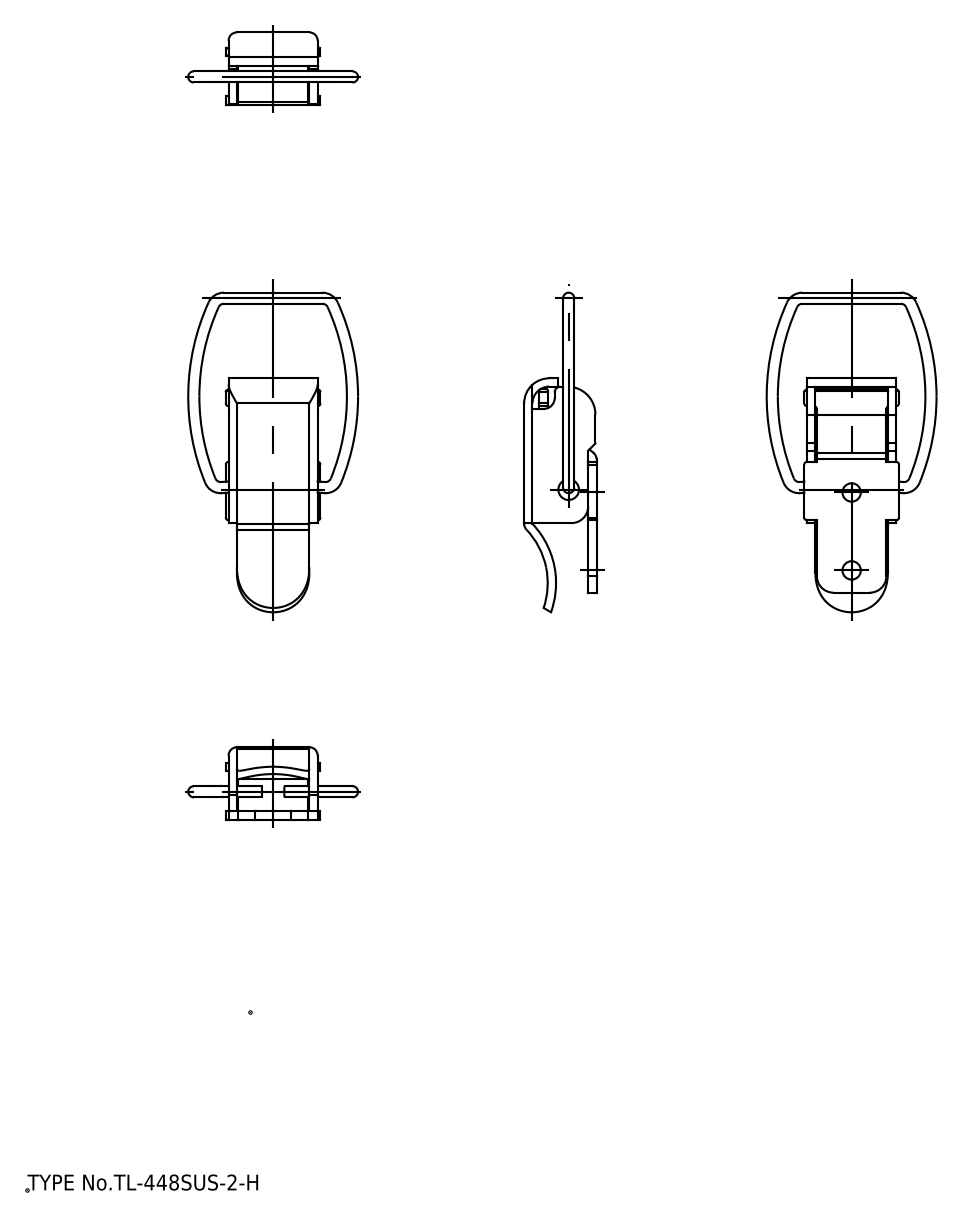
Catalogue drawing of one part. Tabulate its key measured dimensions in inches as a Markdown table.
| quantity | value |
| --- | --- |
| part name | アーム; ベース; レバー |
| STEP written by | spGate 20.6.3 (****-****-****-****) (AUTOMOTIVE_DESIGN) |
| units | inches |
| bodies | 3 solids, 110 faces (51 planar, 47 cylindrical, 12 other) |
| overall size | 2.259 × 1.201 × 0.512 |
| volume | 0.171 in³ |
| surface area | 6.91 in² |
| round holes (diameter × count) | 0.13 × 2, 0.146 × 1 |
| round bosses / shafts (diameter × count) | 0.079 × 3 |
| partial cylindrical surfaces (radius × count) | 0.02 × 10, 0.059 × 6, 0.118 × 4, 0.008 × 2, 0.039 × 1, 0.079 × 1, 0.177 × 1, 0.197 × 1 |
| main face-to-face distances | 0.059, 0.453, 0.512, 0.571, 0.394, 0.63, 0.108, 0.344, 0.069, 0.561 |
| hole center spacings | 0.551 |
